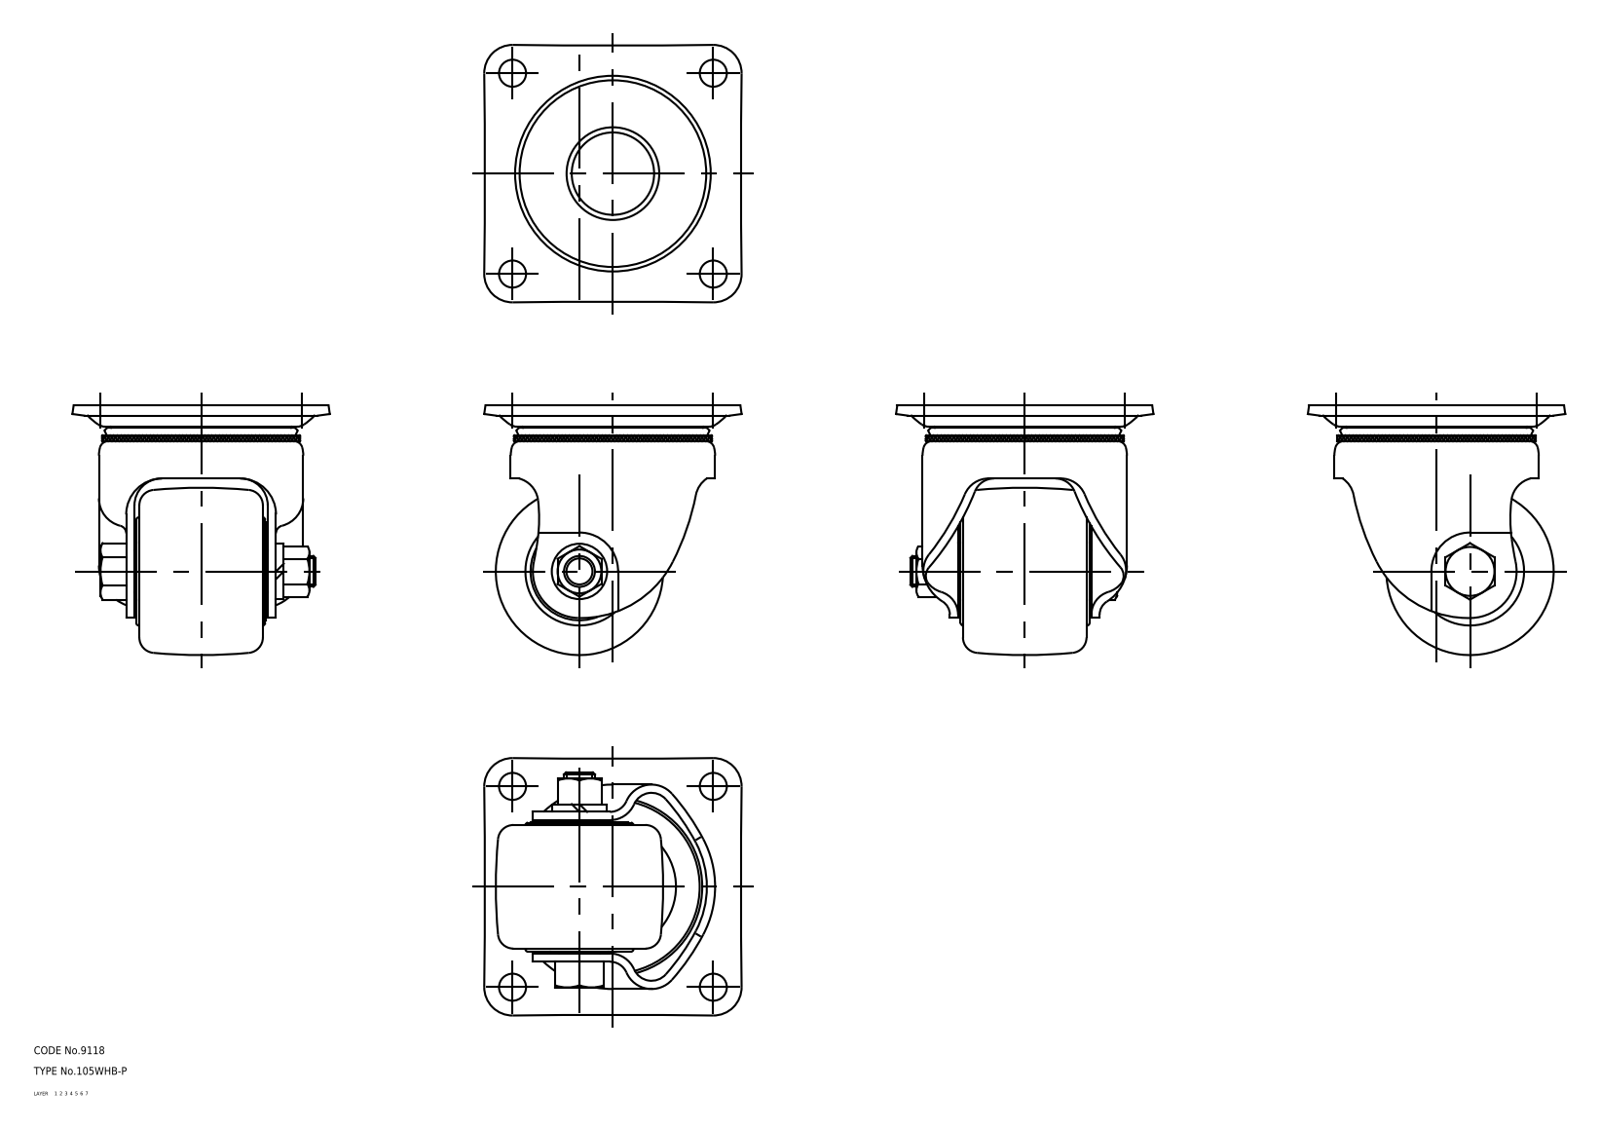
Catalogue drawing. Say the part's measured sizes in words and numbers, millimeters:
The part is named "67129728; 67129741; 67129754; 67129767 (+1 more)". Its 3-D file was written by "CADfix (AUTOMOTIVE_DESIGN)". It is 5 solids with 277 faces: 0 planar, 0 cylindrical and 277 other. Overall it measures 100 by 100 by 97 millimeters. Its volume is 312 861 cubic millimeters and its surface area 81 324 square millimeters.
